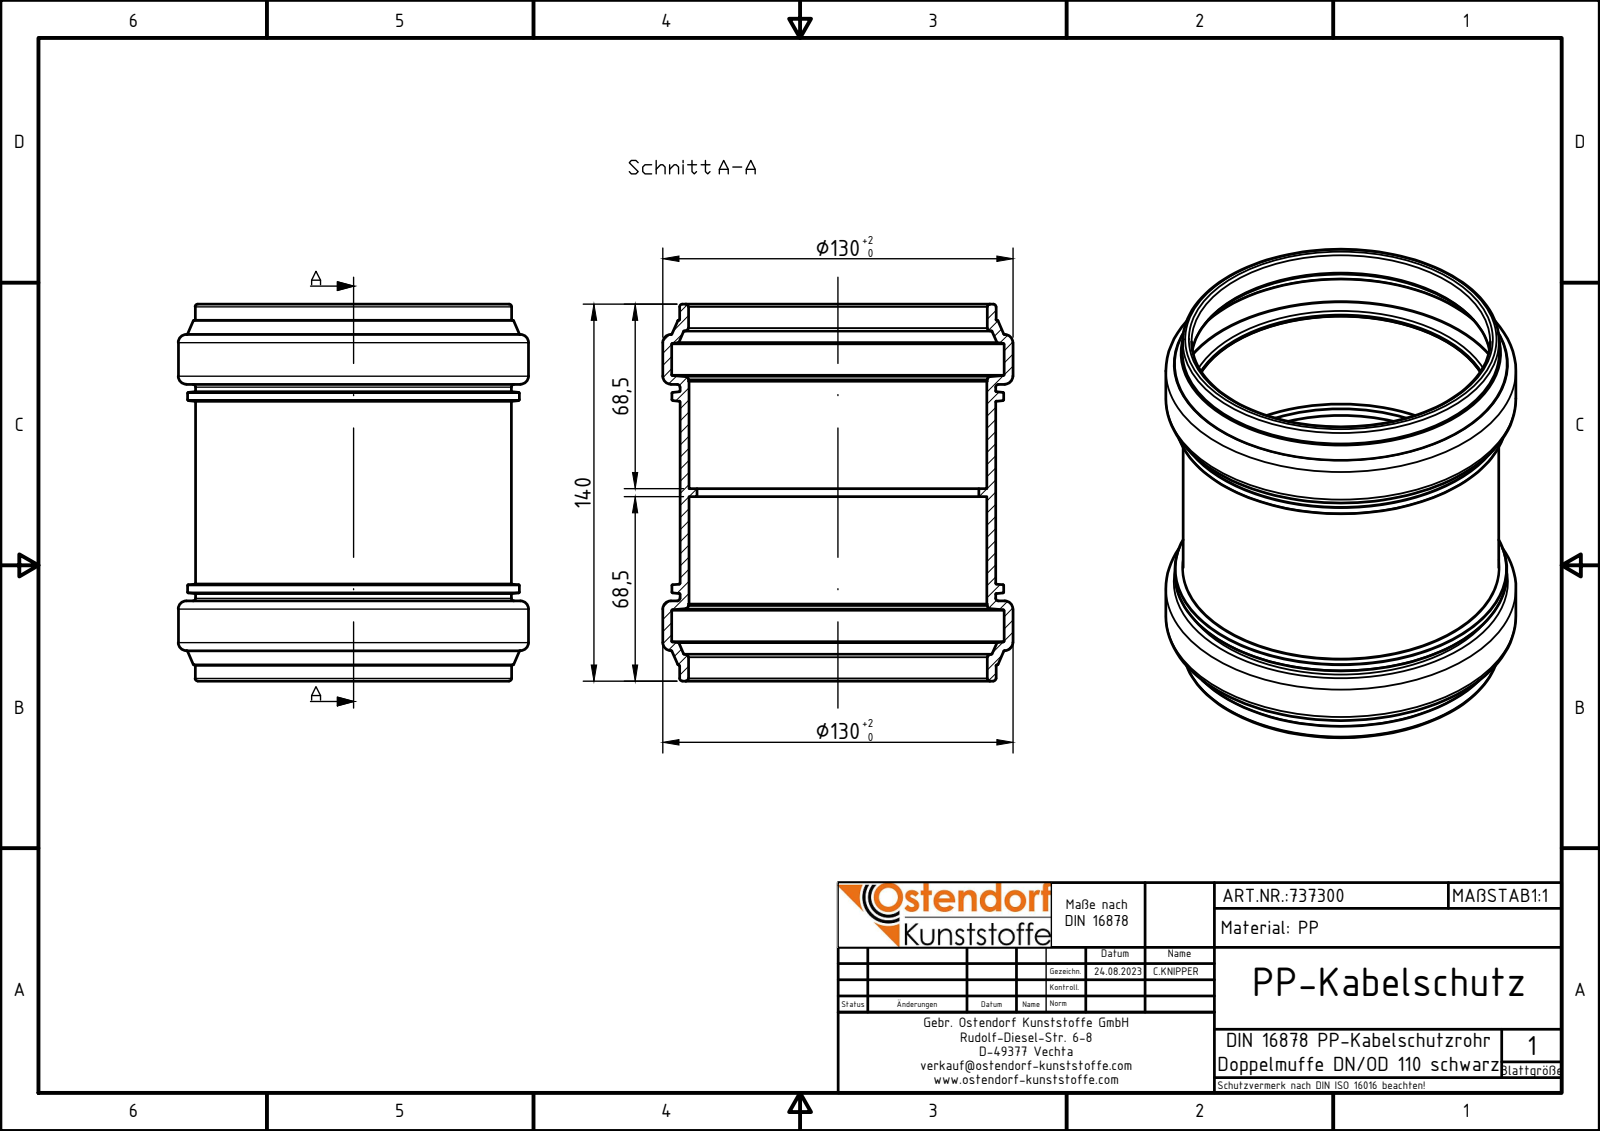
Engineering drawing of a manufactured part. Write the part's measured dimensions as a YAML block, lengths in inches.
part_name: "737300z"
step_written_by: "Autodesk Inventor 2024 (AUTOMOTIVE_DESIGN)"
units: inches
bodies: {solids: 1, faces: 80, planar: 12, cylindrical: 18, other: 50}
overall_size: [5.512, 5.118, 5.118]
volume: 12.45
surface_area: 191.2
round_holes:
  - {diameter: 4.118, count: 1}
  - {diameter: 4.354, count: 1}
  - {diameter: 4.366, count: 1}
  - {diameter: 4.858, count: 1}
round_bosses_or_shafts:
  - {diameter: 5.118, count: 1}
  - {diameter: 4.85, count: 1}
  - {diameter: 4.626, count: 1}
  - {diameter: 4.614, count: 1}
face_to_face_distances: [1.524, 1.642, 0.118, 1.173, 2.697, 2.815, 4.339, 3.165, 5.512, 1.128]
